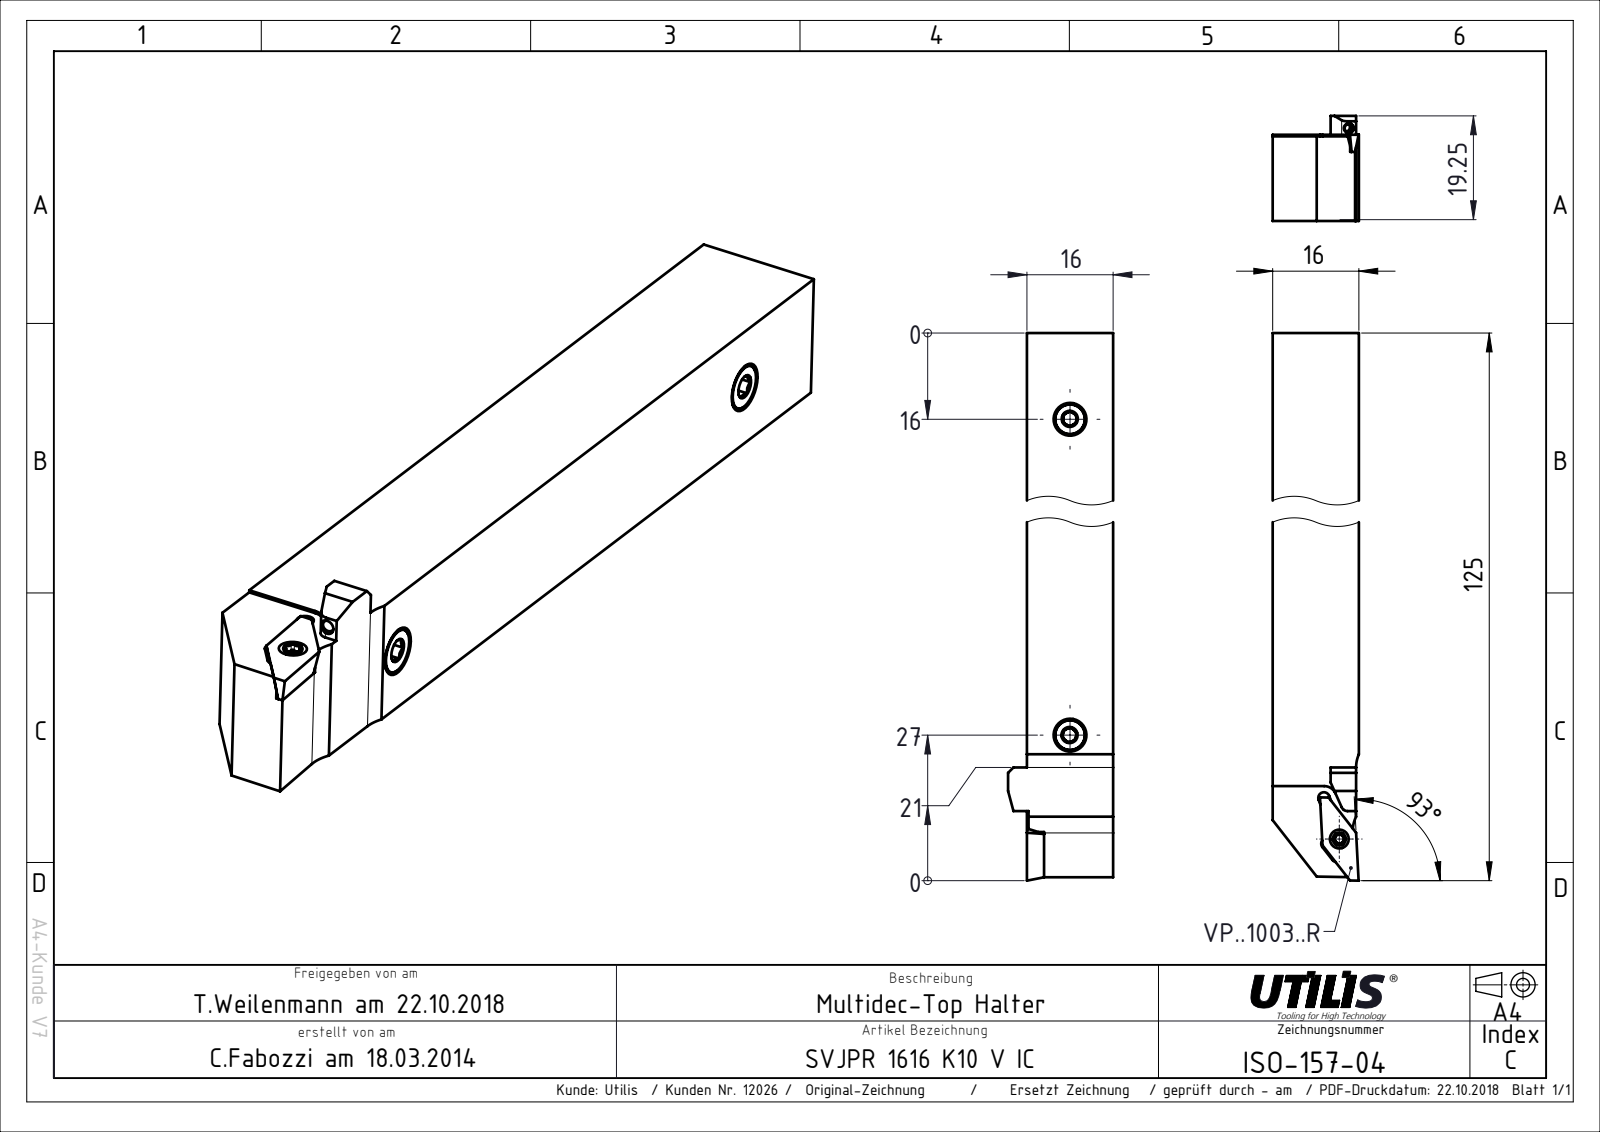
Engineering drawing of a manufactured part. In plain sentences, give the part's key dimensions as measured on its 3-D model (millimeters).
The part is named "ISO-157-04". Its 3-D file was written by "SolidWorks 2016 (AUTOMOTIVE_DESIGN)". It is 1 solid with 51 faces: 44 planar, 7 cylindrical and 0 other. Overall it measures 125 by 19.5 by 16.2 millimeters. Its volume is 31 001 cubic millimeters and its surface area 8 461 square millimeters. Partial cylindrical surfaces (rounded edges, fillets, slot ends): 3 of radius 1.05, 2 of radius 6.1, 1 of radius 2.3. The main face-to-face distances are 16, 15.73, 15.7, 19.5, 3.8, 3.5, 12.82, 2.88, 3.18, 6.68.
